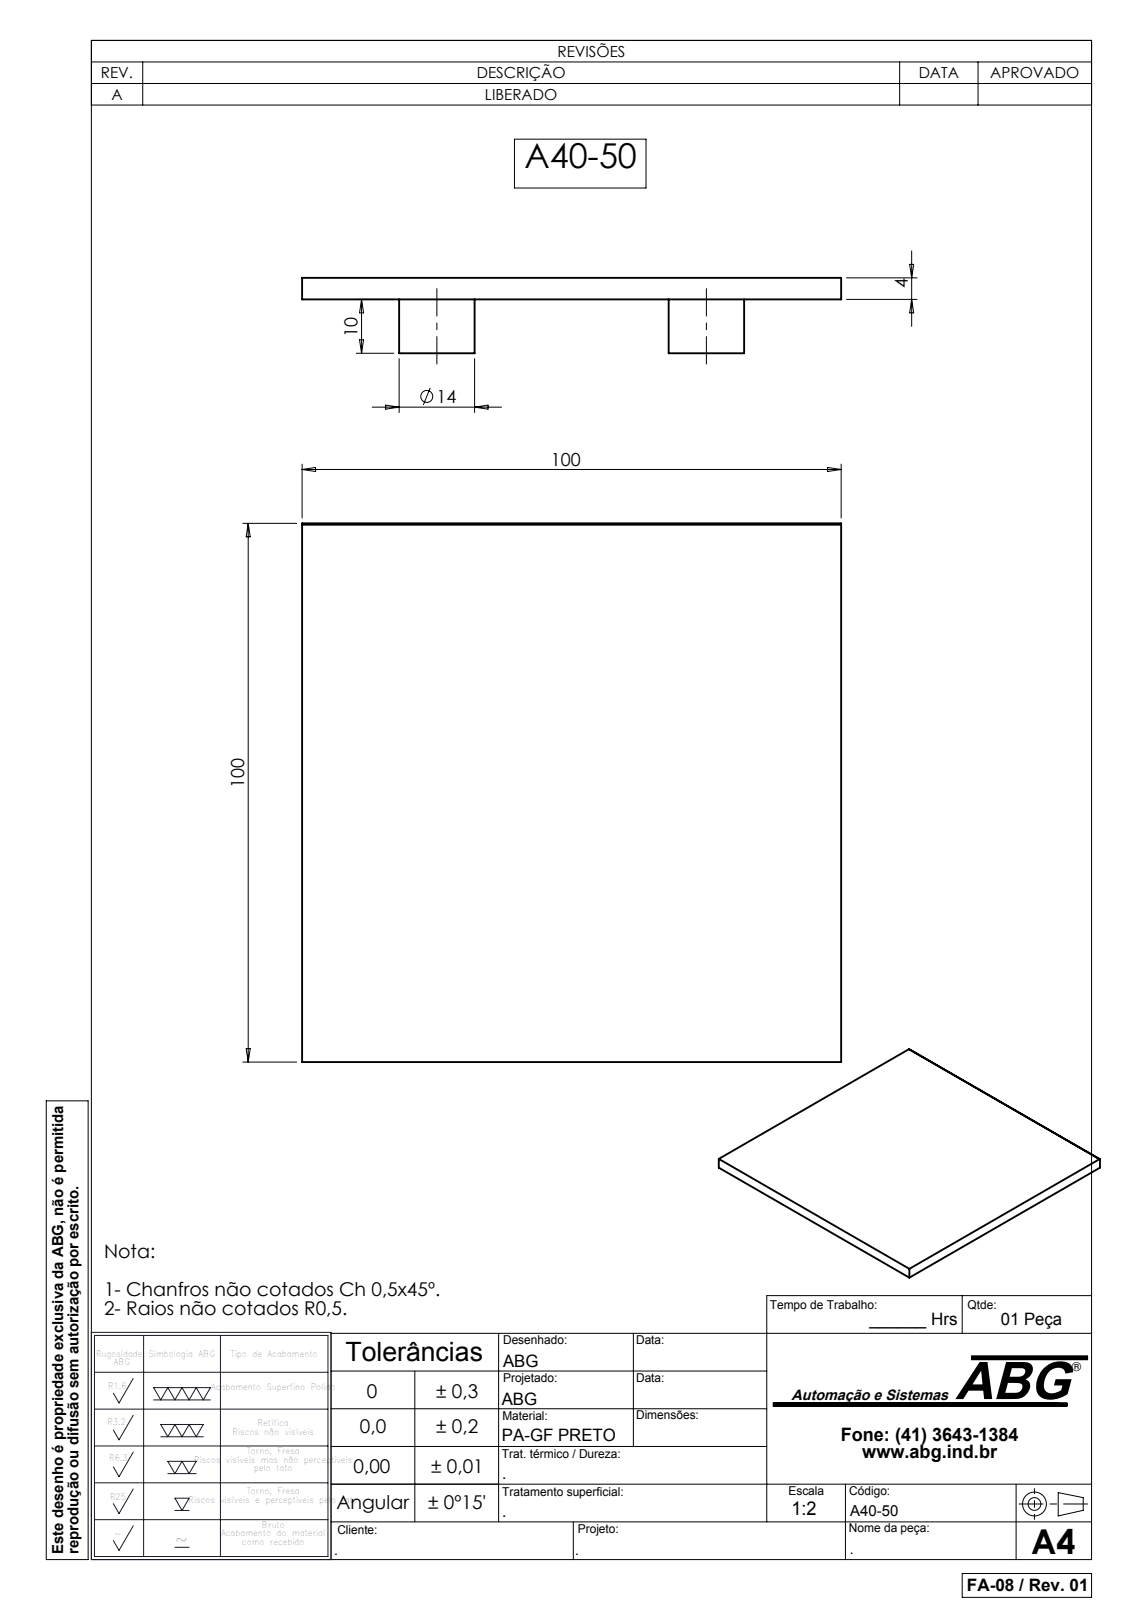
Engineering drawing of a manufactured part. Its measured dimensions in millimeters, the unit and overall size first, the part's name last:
Units: millimetres
Overall size (bounding box): 100 × 100 × 14
Round holes (diameter × count): ⌀12 ×4
Round bosses / shafts (diameter × count): ⌀14 ×4
Partial cylindrical surfaces — rounded edges, fillets, slot ends (radius × count): R0.25 ×1
Main face-to-face distances: 4, 100, 14, 10
Hole centre spacings: 50, 70.71
Volume: 41 632 mm³ · Surface area: 24 856 mm²
Bodies: 1 solid, 31 faces (14 planar, 17 cylindrical, 0 other)
Part name (STEP PRODUCT): A40-50
STEP written by: SolidWorks 2007 (CONFIG_CONTROL_DESIGN)
